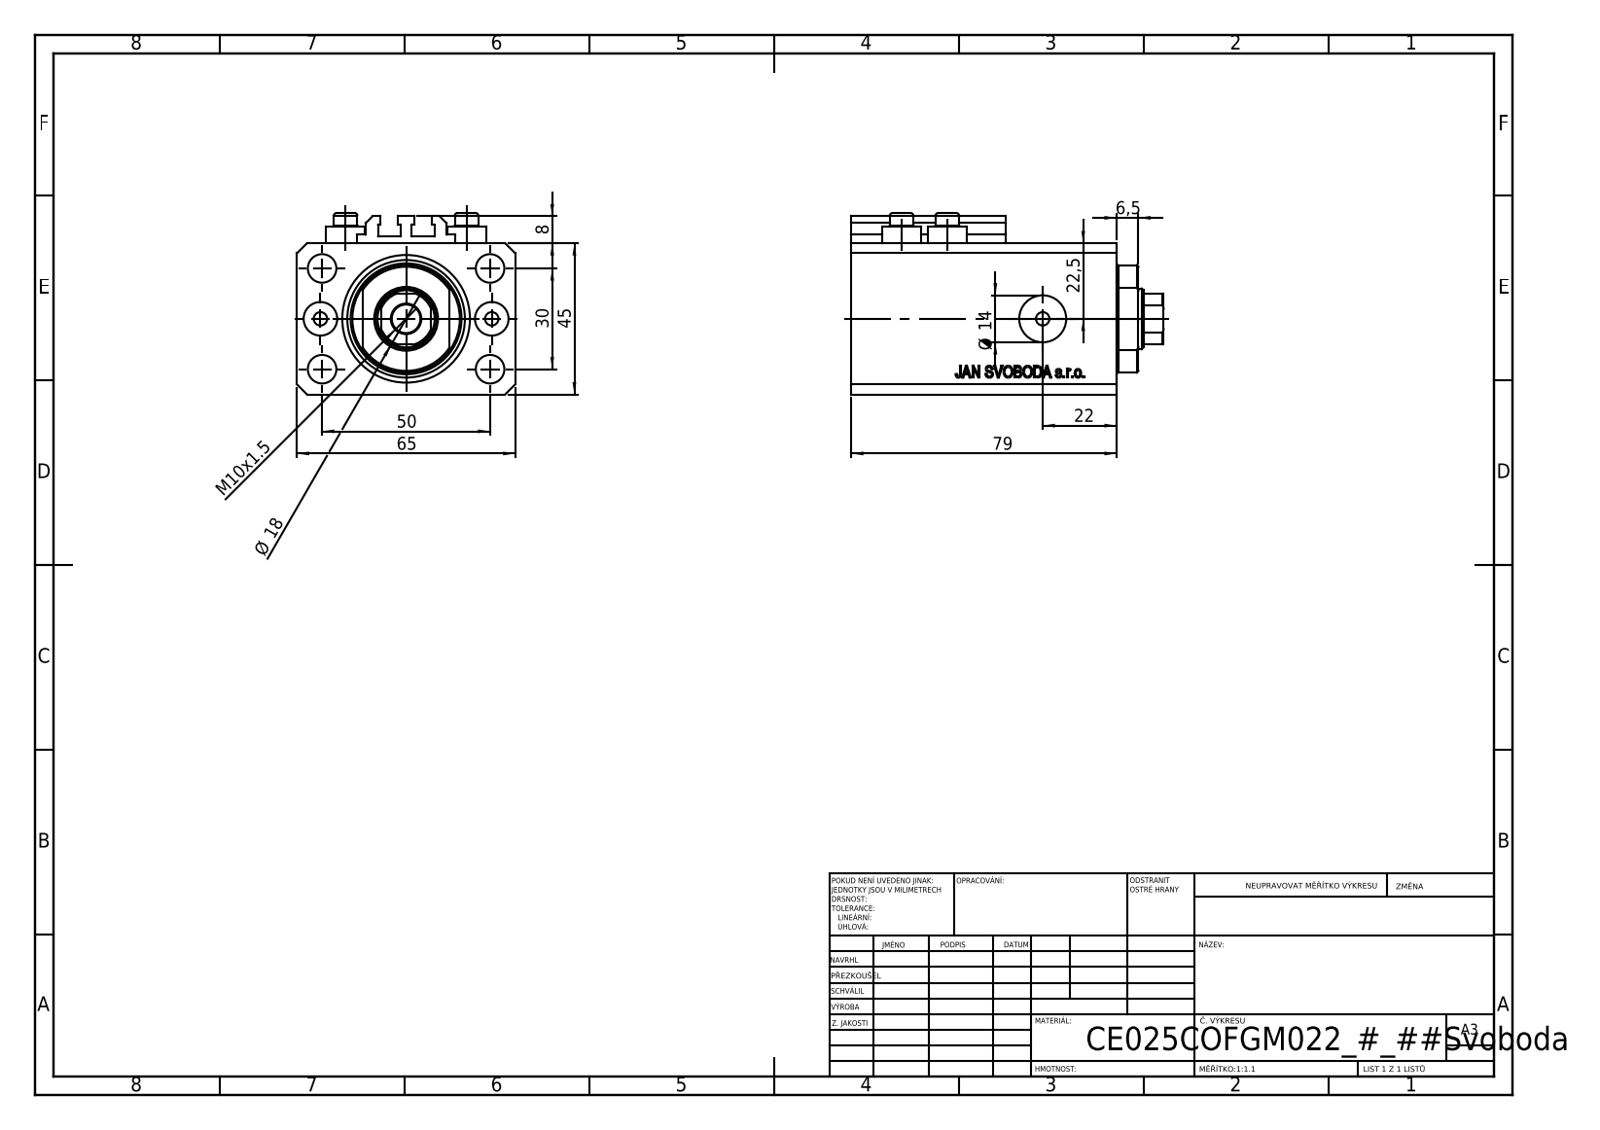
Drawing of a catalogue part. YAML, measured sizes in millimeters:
part_name: "V250CE_VC_C; ALLEN BOLT V250CE; V250CE_C_VCP; V250CE_C_Body"
step_written_by: "SolidWorks 2019 (CONFIG_CONTROL_DESIGN)"
units: millimeters
bodies: {solids: 8, faces: 1034, planar: 504, cylindrical: 86, other: 444}
overall_size: [93, 65, 54]
volume: 217078
surface_area: 58377
round_holes:
  - {diameter: 4, count: 8}
  - {diameter: 8.5, count: 5}
  - {diameter: 10, count: 2}
  - {diameter: 14, count: 2}
  - {diameter: 18, count: 1}
  - {diameter: 25, count: 1}
  - {diameter: 38, count: 1}
round_bosses_or_shafts:
  - {diameter: 11.6, count: 4}
  - {diameter: 7, count: 4}
partial_cylinders:
  - {radius: 0.2, count: 10}
  - {radius: 8.5, count: 1}
  - {radius: 16, count: 1}
face_to_face_distances: [45, 65, 14, 79, 3, 6.9, 58.1, 72.1, 47, 20.5]
hole_center_spacings: [15.01, 29.15, 52.68, 13.6, 25.5, 30, 36, 38.48]
